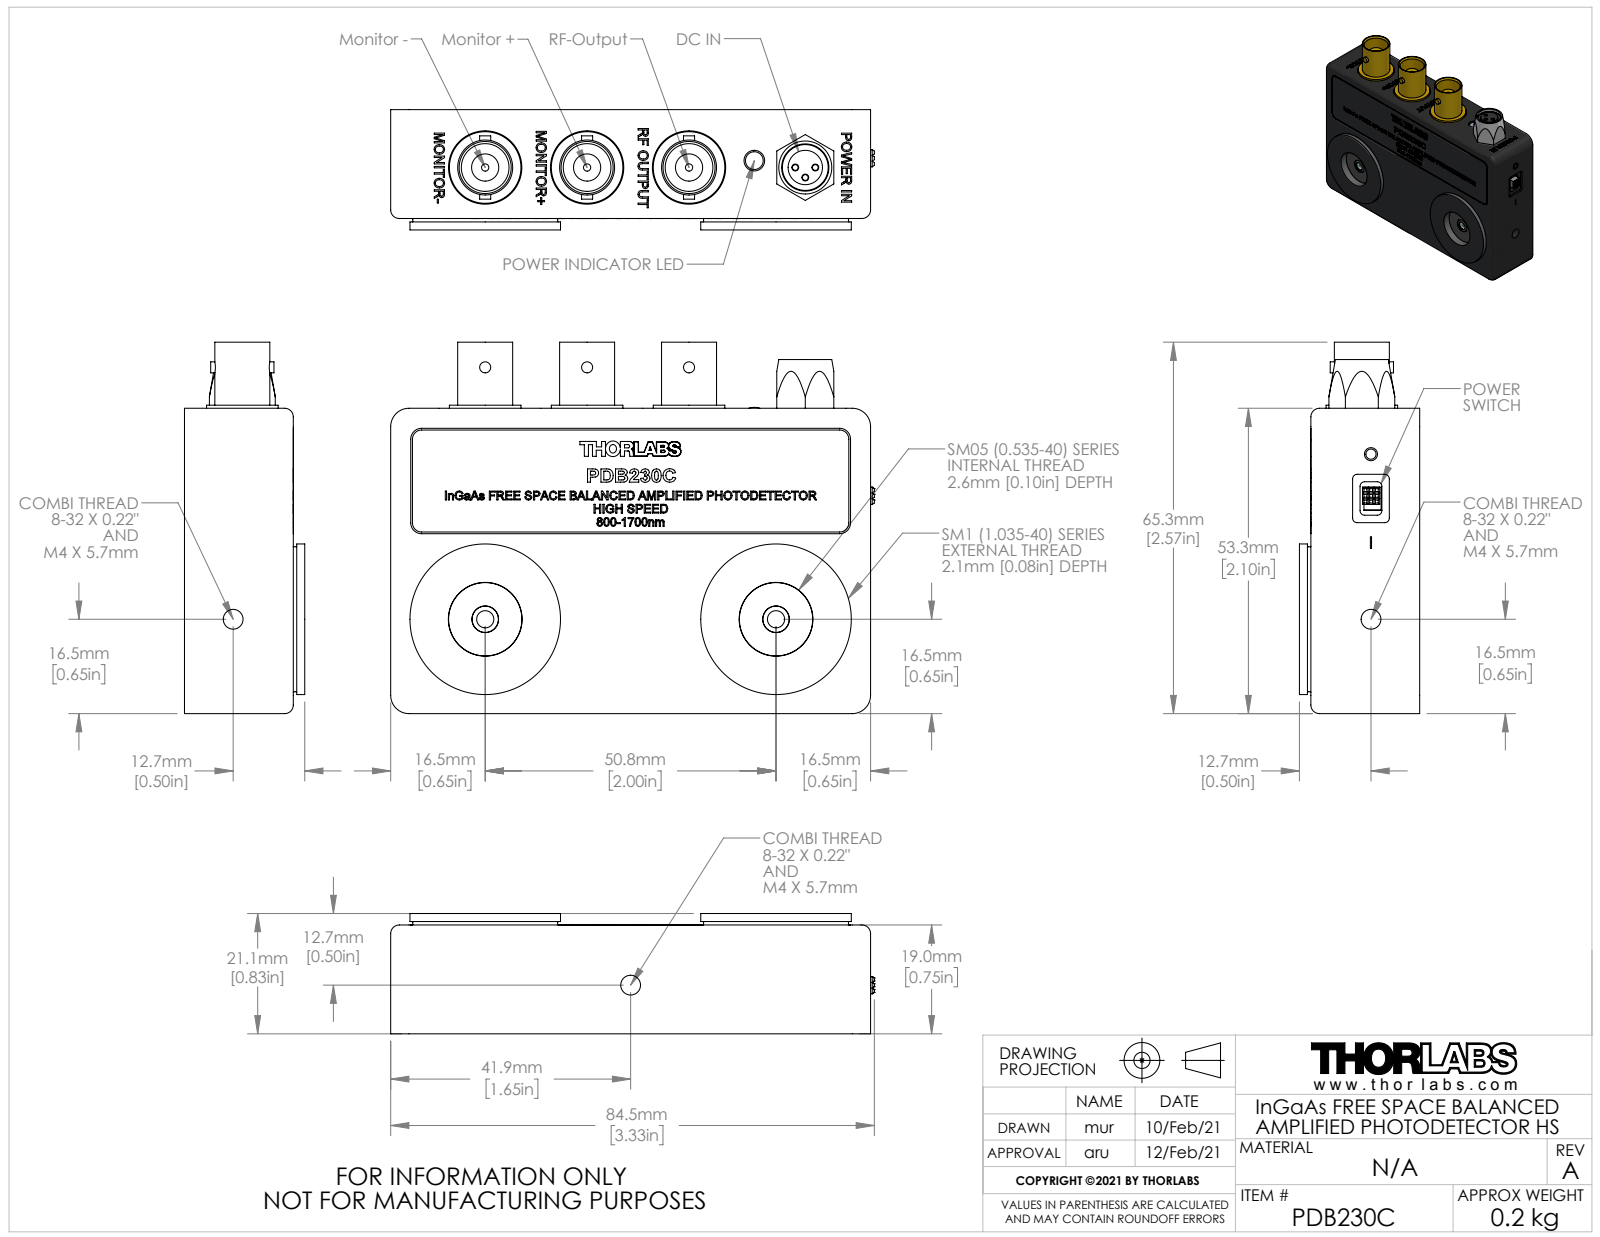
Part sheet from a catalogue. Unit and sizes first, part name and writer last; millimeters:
Units: millimetres
Overall size (bounding box): 84.46 × 64.83 × 21
Round holes (diameter × count): ⌀1.6 ×9, ⌀0.7 ×8, ⌀0.75 ×6, ⌀1.02 ×6, ⌀0.51 ×5, ⌀0.2 ×4, ⌀2.4 ×4, ⌀1 ×3, ⌀1.27 ×3, ⌀2.3 ×3, ⌀8.33 ×3, ⌀12.2 ×3
Round bosses / shafts (diameter × count): ⌀0.43 ×6, ⌀2 ×4, ⌀12.5 ×3, ⌀9.6 ×3, ⌀9.4 ×3, ⌀4.75 ×3, ⌀4 ×3, ⌀2.3 ×3
Partial cylindrical surfaces — rounded edges, fillets, slot ends (radius × count): R3.2 ×31, R0.15 ×24, R0.4 ×24, R3.3 ×14, R0.8 ×8, R0.5 ×6, R1.9 ×6, R2.5 ×5
Main face-to-face distances: 1.59, 11.43, 18.99, 17.4, 1.58, 5.97, 13.02, 1.8, 4.17, 17.19
Hole centre spacings: 1.11, 1.8, 2, 3.2, 16.65, 38.26, 1.75, 2.5
Volume: 37 266 mm³ · Surface area: 40 789 mm²
Bodies: 17 solids, 6080 faces (3605 planar, 330 cylindrical, 2145 other)
Part name (STEP PRODUCT): 21.04.13_PDB230C_WEB
STEP written by: SolidWorks 2019 (AUTOMOTIVE_DESIGN)
